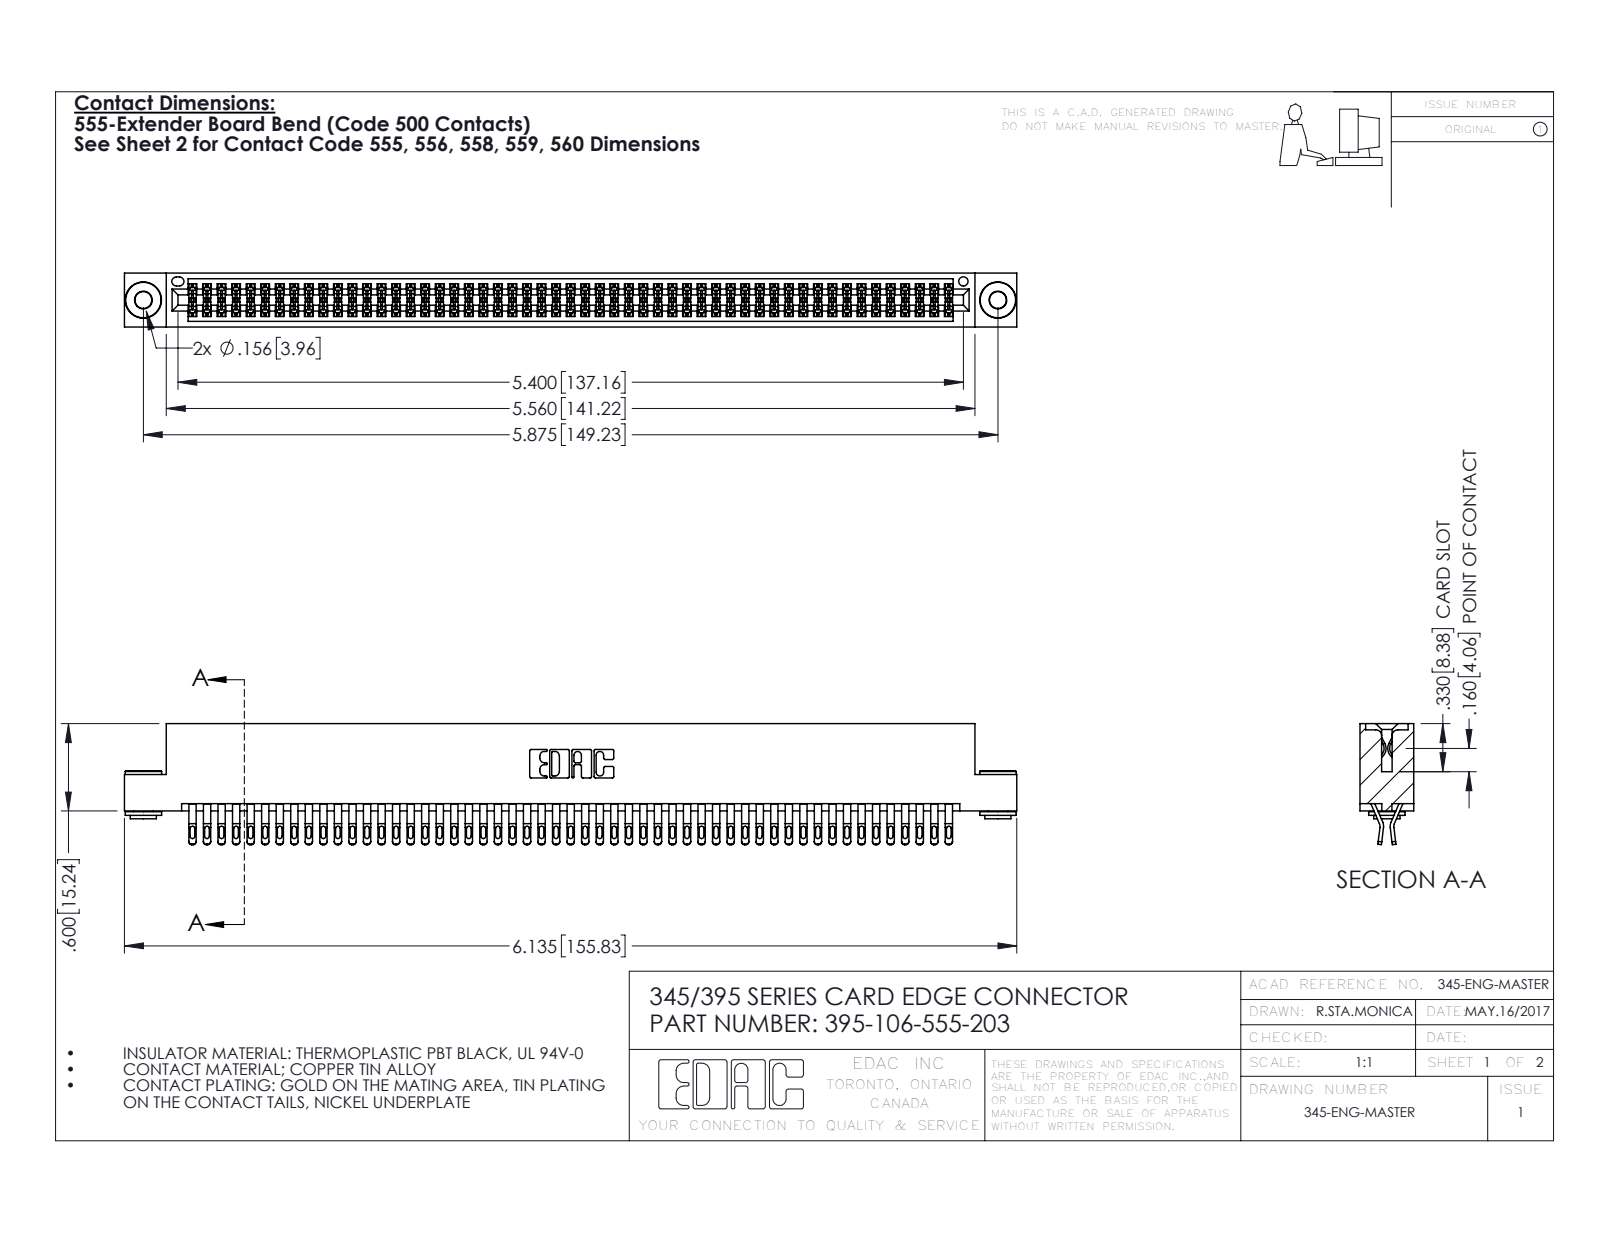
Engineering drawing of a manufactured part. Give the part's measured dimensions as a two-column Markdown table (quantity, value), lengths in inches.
| quantity | value |
| --- | --- |
| part name | 345 Part_Flush Mounting Lugs - 0.156 Dia-TH; 345-250-002_345-250-002-102; 395-106-555-203; 345-292-001_555 Tail |
| STEP written by | SolidWorks 2016 (CONFIG_CONTROL_DESIGN) |
| units | inches |
| bodies | 109 solids, 6100 faces (3376 planar, 2716 cylindrical, 8 other) |
| overall size | 6.135 × 0.832 × 0.37 |
| volume | 0.95 in³ |
| surface area | 37.97 in² |
| round holes (diameter × count) | 0.116 × 2, 0.156 × 2, 0.064 × 1 |
| round bosses / shafts (diameter × count) | 0.25 × 2, 0.18 × 2, 0.136 × 2 |
| partial cylindrical surfaces (radius × count) | 0.016 × 265, 0.02 × 212, 0.006 × 159, 0.01 × 22, 0.007 × 6, 0.031 × 6, 0.026 × 3, 0.01 × 2 |
| main face-to-face distances | 0.072, 0.298, 0.025, 0.2, 0.37, 0.098, 0.272, 0.225, 0.175, 0.149 |
| hole center spacings | 0.27, 5.639, 5.875 |
